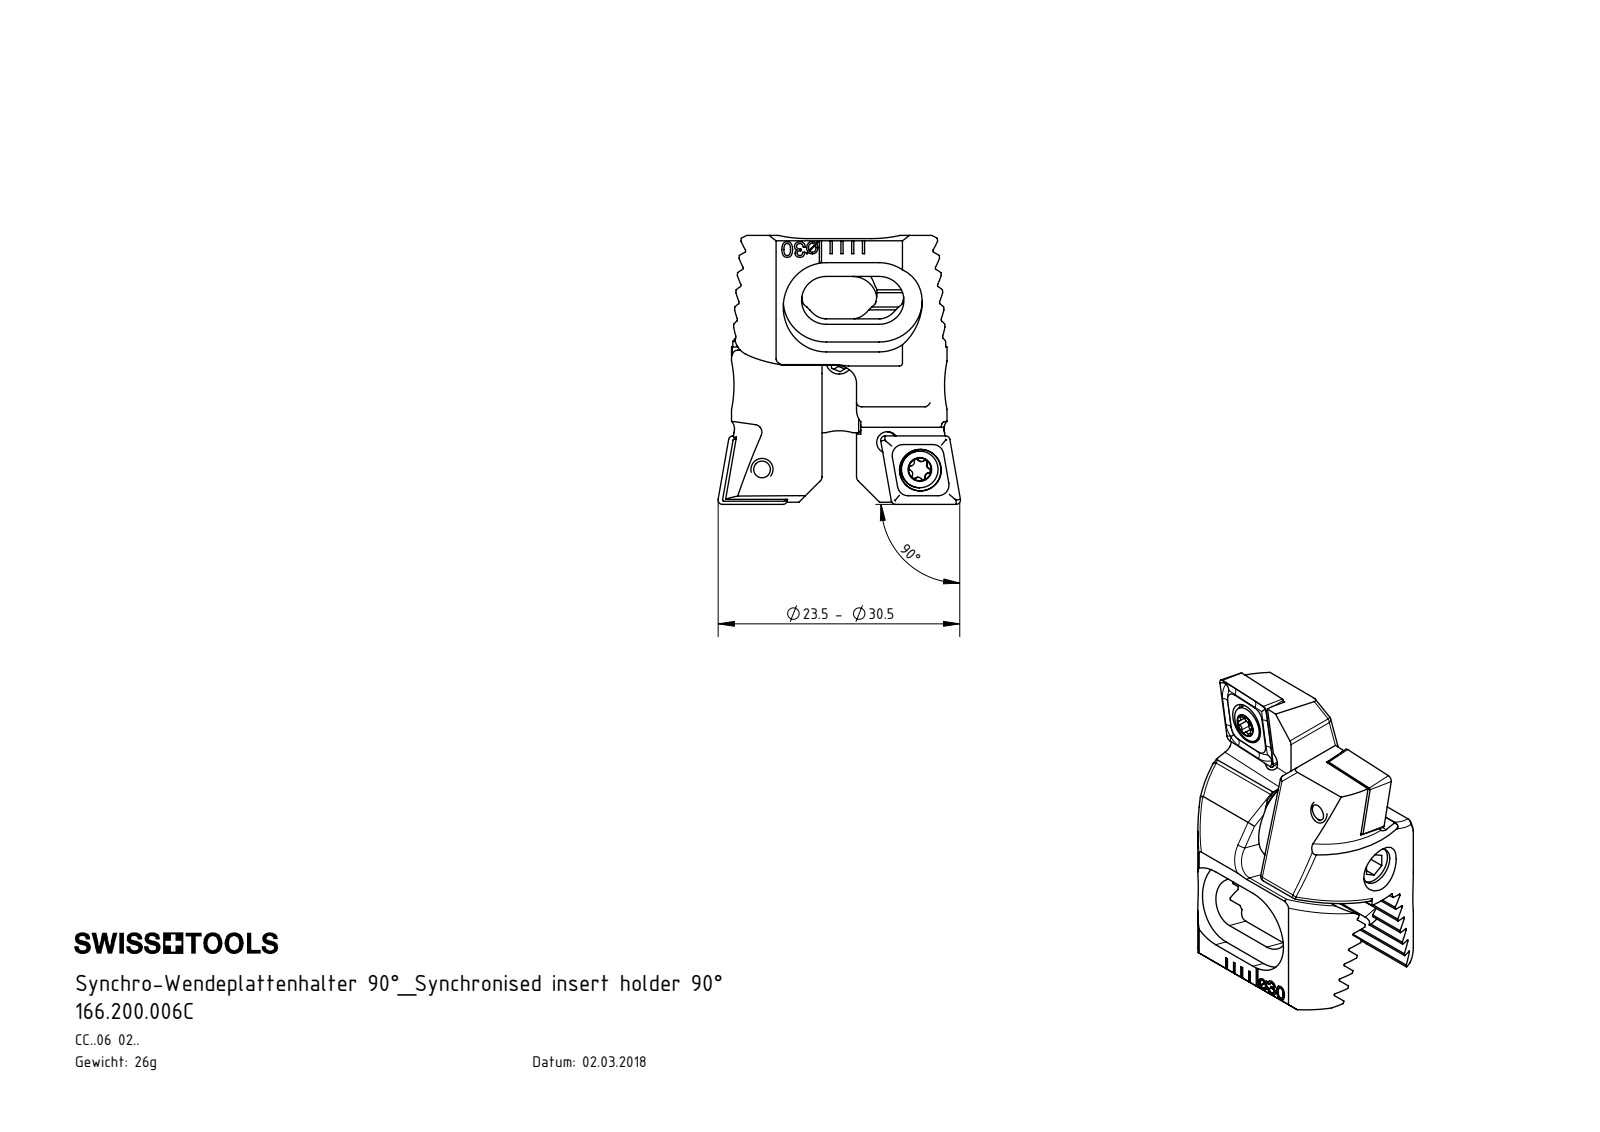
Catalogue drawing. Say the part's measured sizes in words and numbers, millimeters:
The part is named "Z20-WCA.001.015_A; Z20-ER3.002.004_A; CCMT060204; WCA-ER2.001.006_A (+4 more)". Its 3-D file was written by "SolidWorks 2017 (CONFIG_CONTROL_DESIGN)". It is 11 solids with 485 faces: 189 planar, 158 cylindrical and 138 other. Overall it measures 24.95 by 22.42 by 16.3 millimeters. Its volume is 3 171 cubic millimeters and its surface area 3 798 square millimeters. Round holes: 3 of diameter 1, 3 of diameter 2.5, 2 of diameter 2, 2 of diameter 2.05, 2 of diameter 2.8, 2 of diameter 3.85, 1 of diameter 3.5, 1 of diameter 9.1. Round bosses or shafts: 4 of diameter 3, 2 of diameter 3.4, 2 of diameter 2.5, 1 of diameter 8.8, 1 of diameter 4. Partial cylindrical surfaces (rounded edges, fillets, slot ends): 12 of radius 0.12, 12 of radius 0.21, 10 of radius 0.36, 8 of radius 1, 4 of radius 0.5, 4 of radius 2.3, 4 of radius 4, 2 of radius 0.36. The main face-to-face distances are 1.43, 2.86, 4.29, 4, 5.72, 2.57, 3.85, 7.14, 5.71, 0.42. The hole center spacings are 3.99, 4.09, 12.02, 12.12, 14.88, 2, 5.99, 6.
